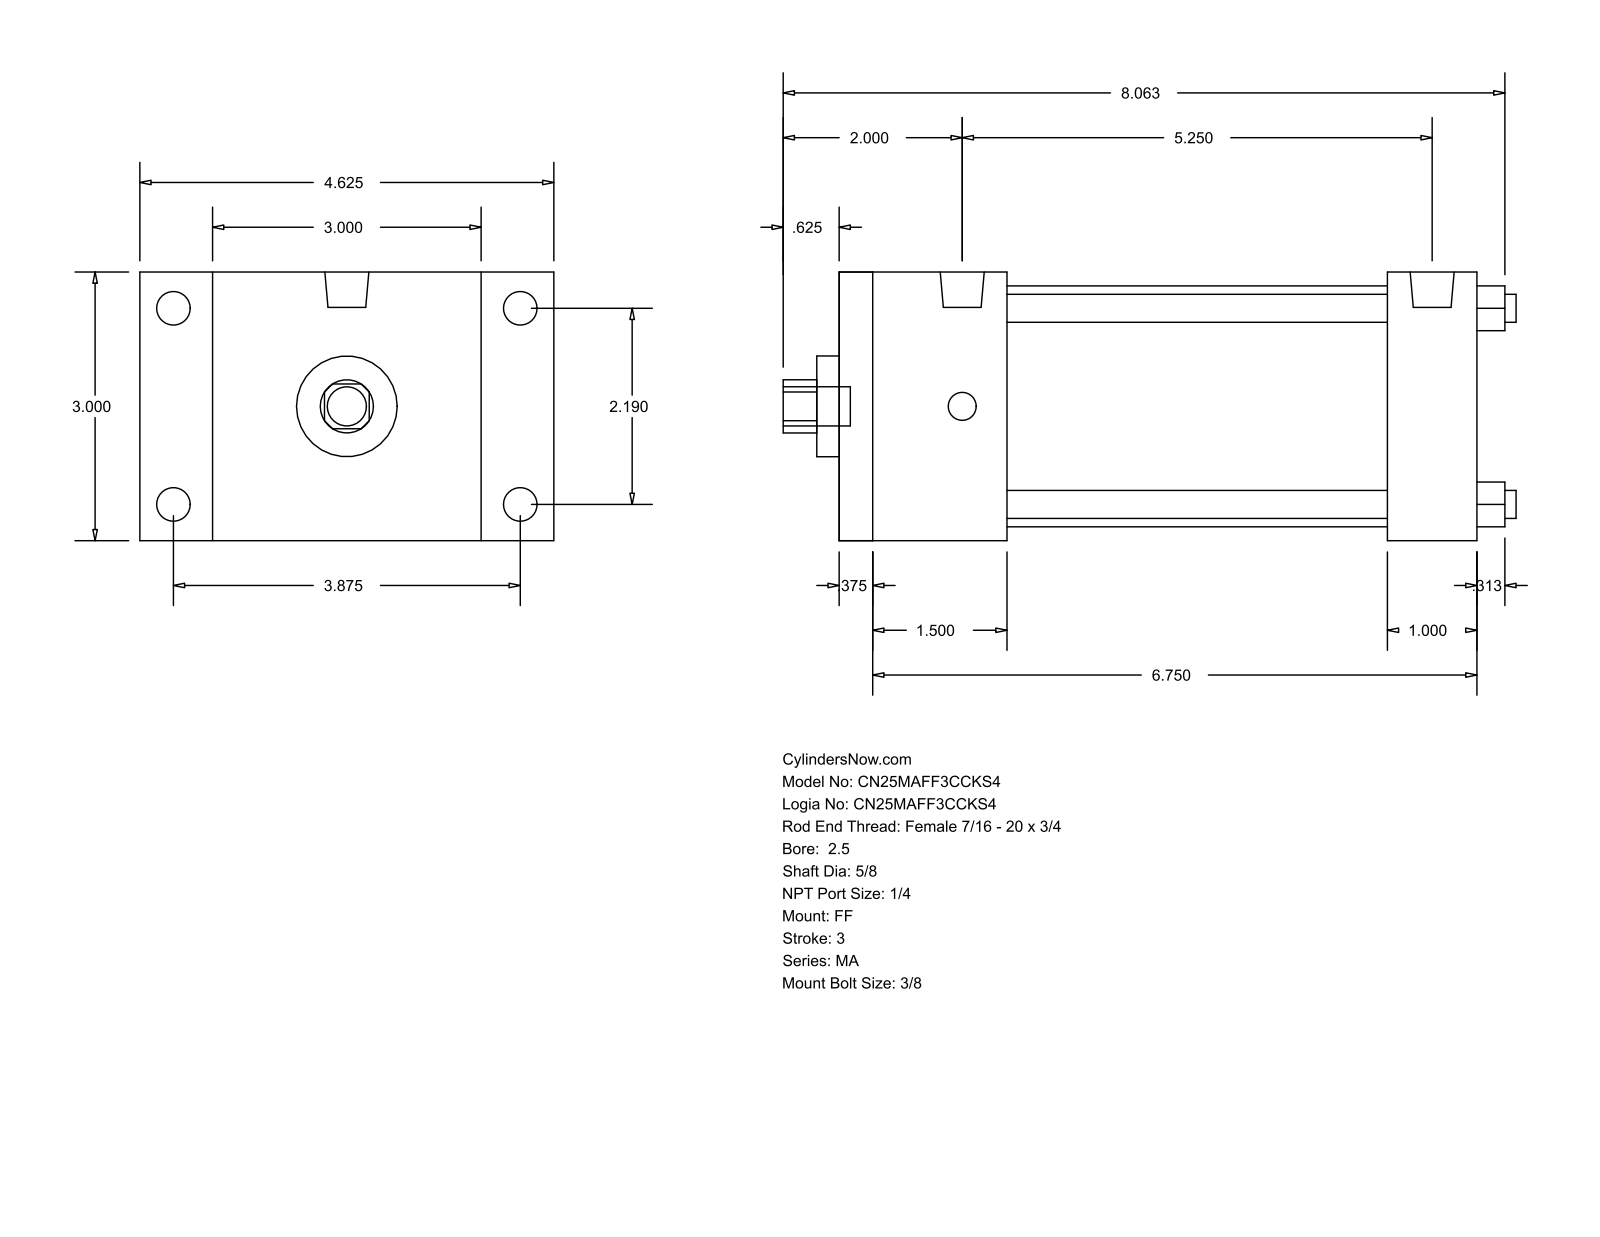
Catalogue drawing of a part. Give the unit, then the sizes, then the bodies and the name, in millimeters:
Units: millimetres
Overall size (bounding box): 207.96 × 117.47 × 76.2
Round holes (diameter × count): ⌀7.94 ×4, ⌀15.88 ×1, ⌀28.57 ×1, ⌀68.33 ×1
Round bosses / shafts (diameter × count): ⌀9.53 ×4, ⌀7.94 ×4, ⌀12.49 ×2, ⌀11.11 ×1
Partial cylindrical surfaces — rounded edges, fillets, slot ends (radius × count): R7.54 ×1
Main face-to-face distances: 76.2, 180.97, 9.52, 171.45, 25.4, 47.62, 155.57, 38.1, 146.05, 107.95
Hole centre spacings: 39.33, 55.62, 78.66
Bodies: 0 solids, 92 faces (64 planar, 28 cylindrical, 0 other)
Part name (STEP PRODUCT): MA_FF__0250_0.625
STEP written by: GSSL Pune (CONFIG_CONTROL_DESIGN)
